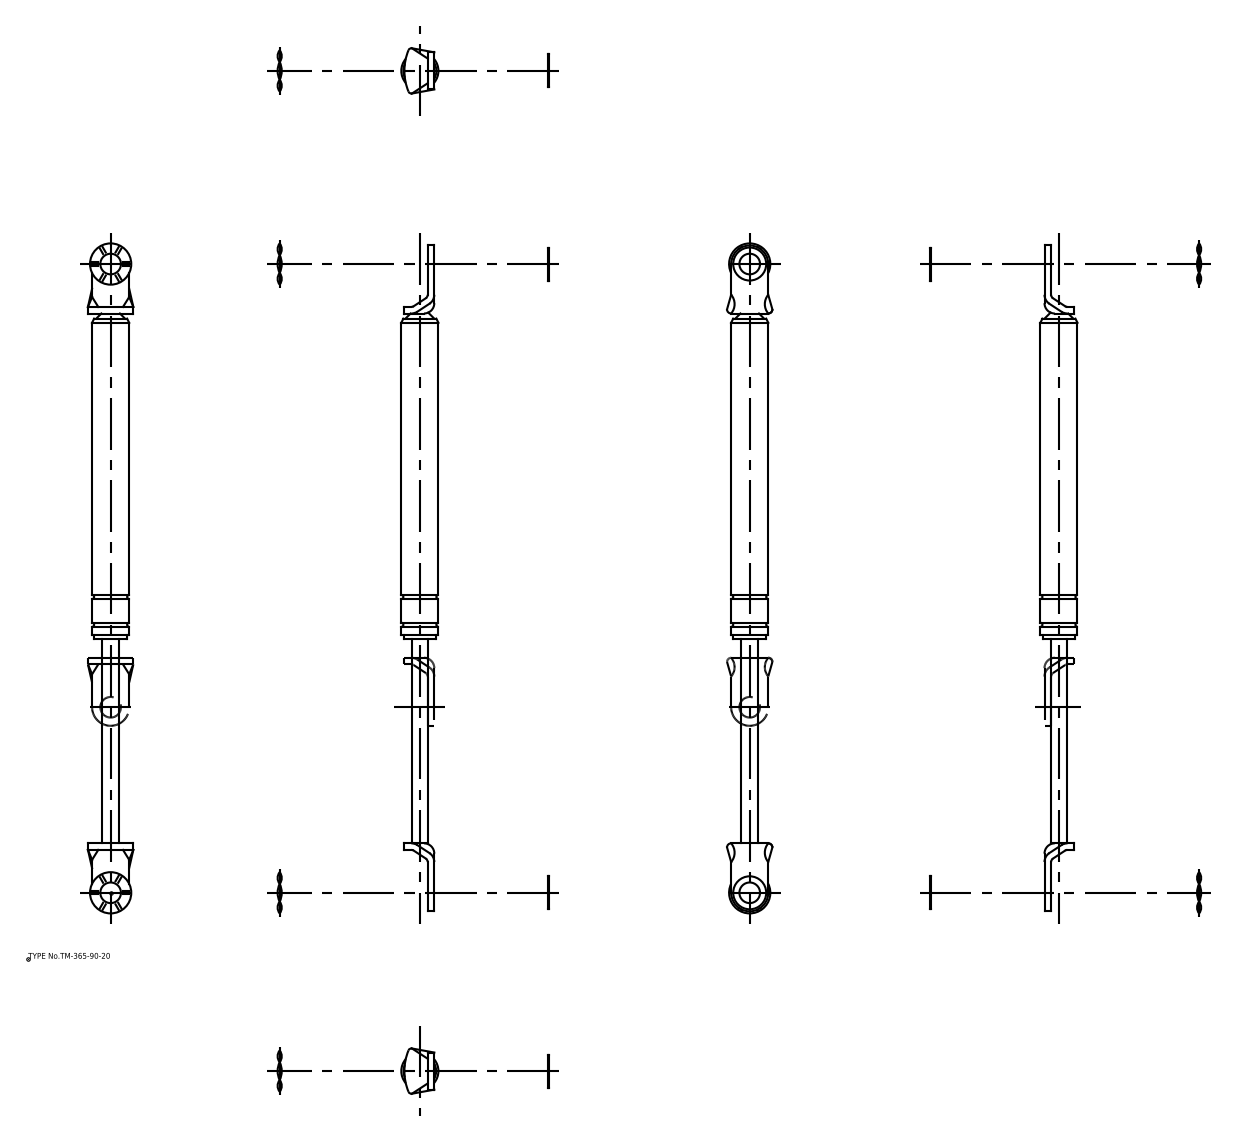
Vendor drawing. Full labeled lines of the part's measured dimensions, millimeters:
Part name (STEP PRODUCT): ウェーブワッシャー; ワッシャー; 本体; 本体_div
STEP written by: spGate 16.7.1 (AUTOMOTIVE_DESIGN)
Units: millimetres
Bodies: 6 solids, 94 faces (42 planar, 44 cylindrical, 8 other)
Overall size (bounding box): 325 × 22 × 18.5
Volume: 50 159 mm³ · Surface area: 17 436 mm²
Round holes (diameter × count): ⌀10 ×2
Round bosses / shafts (diameter × count): ⌀16 ×3, ⌀20 ×2, ⌀18.5 ×1, ⌀18 ×1, ⌀8 ×1
Partial cylindrical surfaces — rounded edges, fillets, slot ends (radius × count): R4.4 ×2, R5 ×2, R9 ×2, R26.32 ×1
Main face-to-face distances: 3.2, 2, 5.2, 260.2, 3.7, 5.7, 0.5, 161.2, 102.2, 263.4
Hole centre spacings: 305
